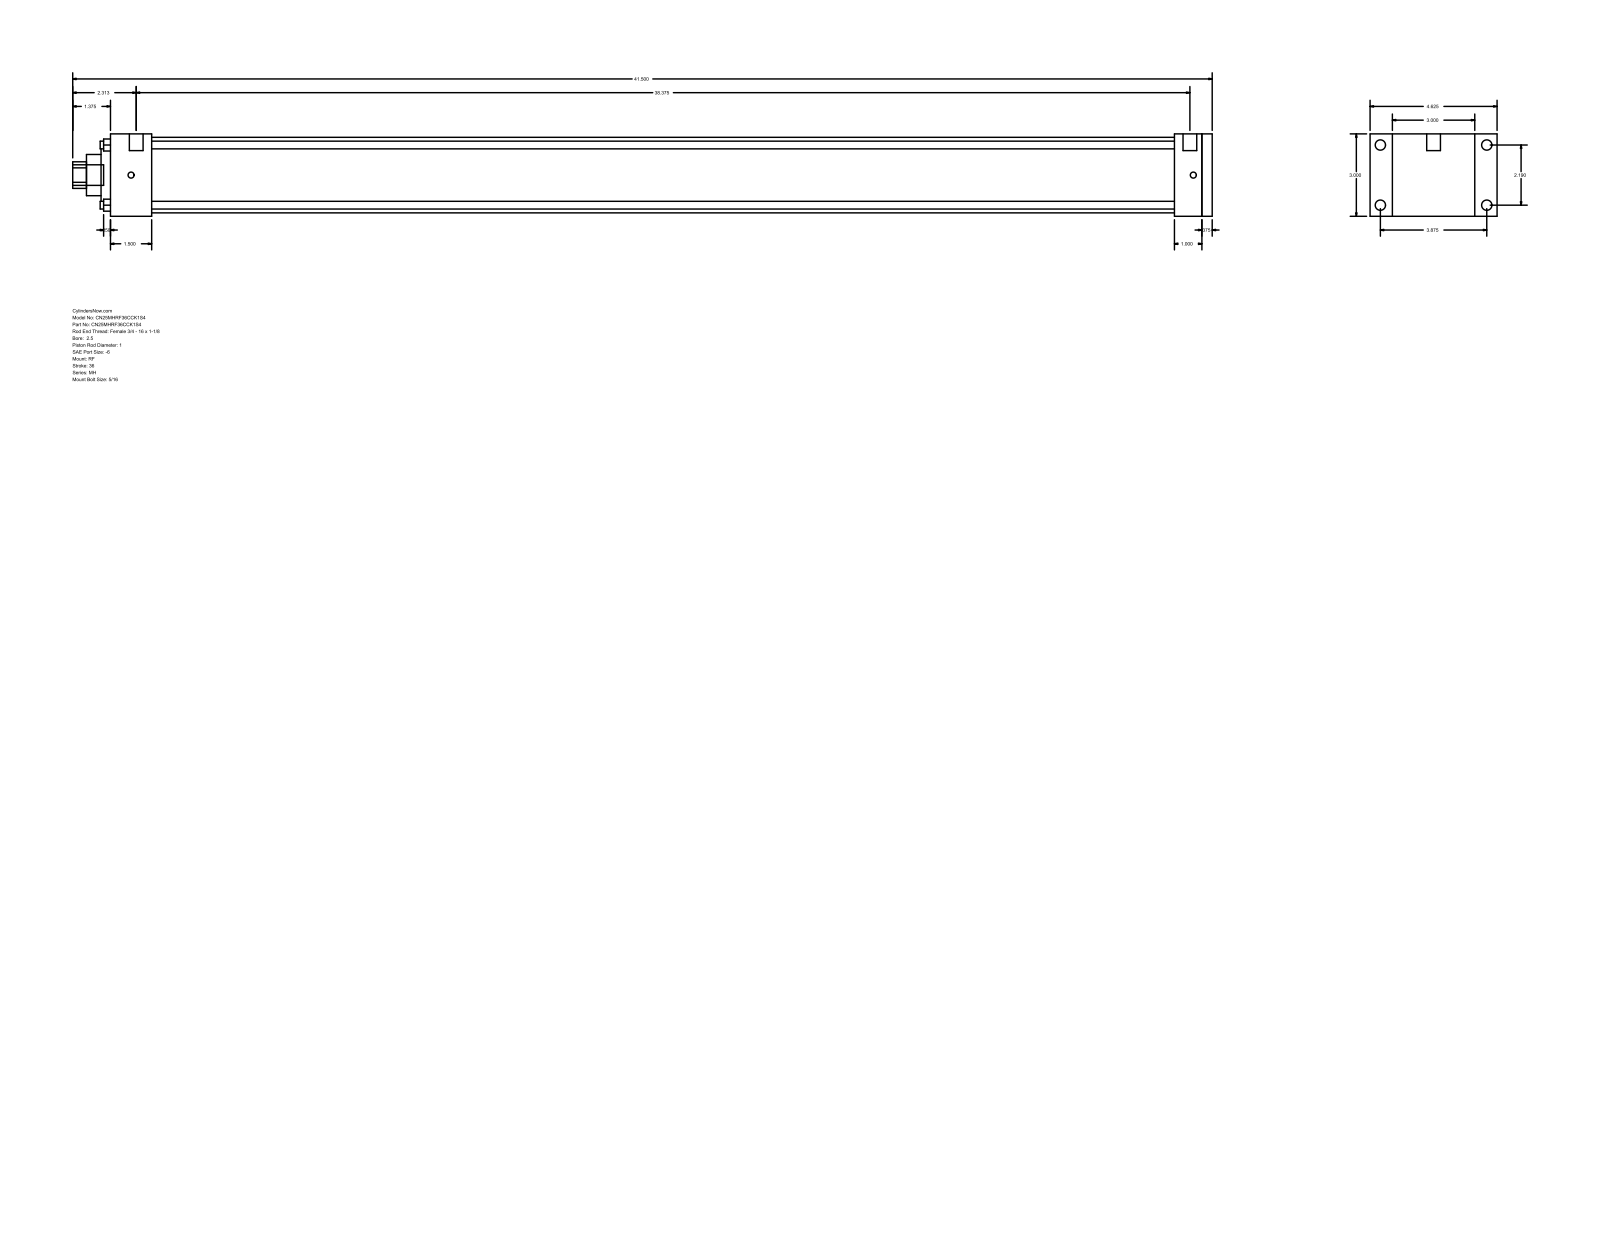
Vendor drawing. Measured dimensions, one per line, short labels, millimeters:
name: MH_RF__0250_1
written by: GSSL Pune (CONFIG_CONTROL_DESIGN)
unit: mm
bodies: 0 solids, 94 faces (65 planar, 29 cylindrical, 0 other)
size: 1054.1 × 117.47 × 76.2
holes: 4× ⌀7.14, 1× ⌀25.4, 1× ⌀38.1, 1× ⌀60.33, 1× ⌀69.85
bosses: 4× ⌀9.53, 4× ⌀5.56, 2× ⌀12.7, 1× ⌀19.05
rounds: 1× R12.29
face distances: 76.2, 9.52, 1019.18, 1009.66, 984.25, 25.41, 34.93, 38.11, 946.14, 971.55
hole spacings: 39.33, 55.62, 78.66
